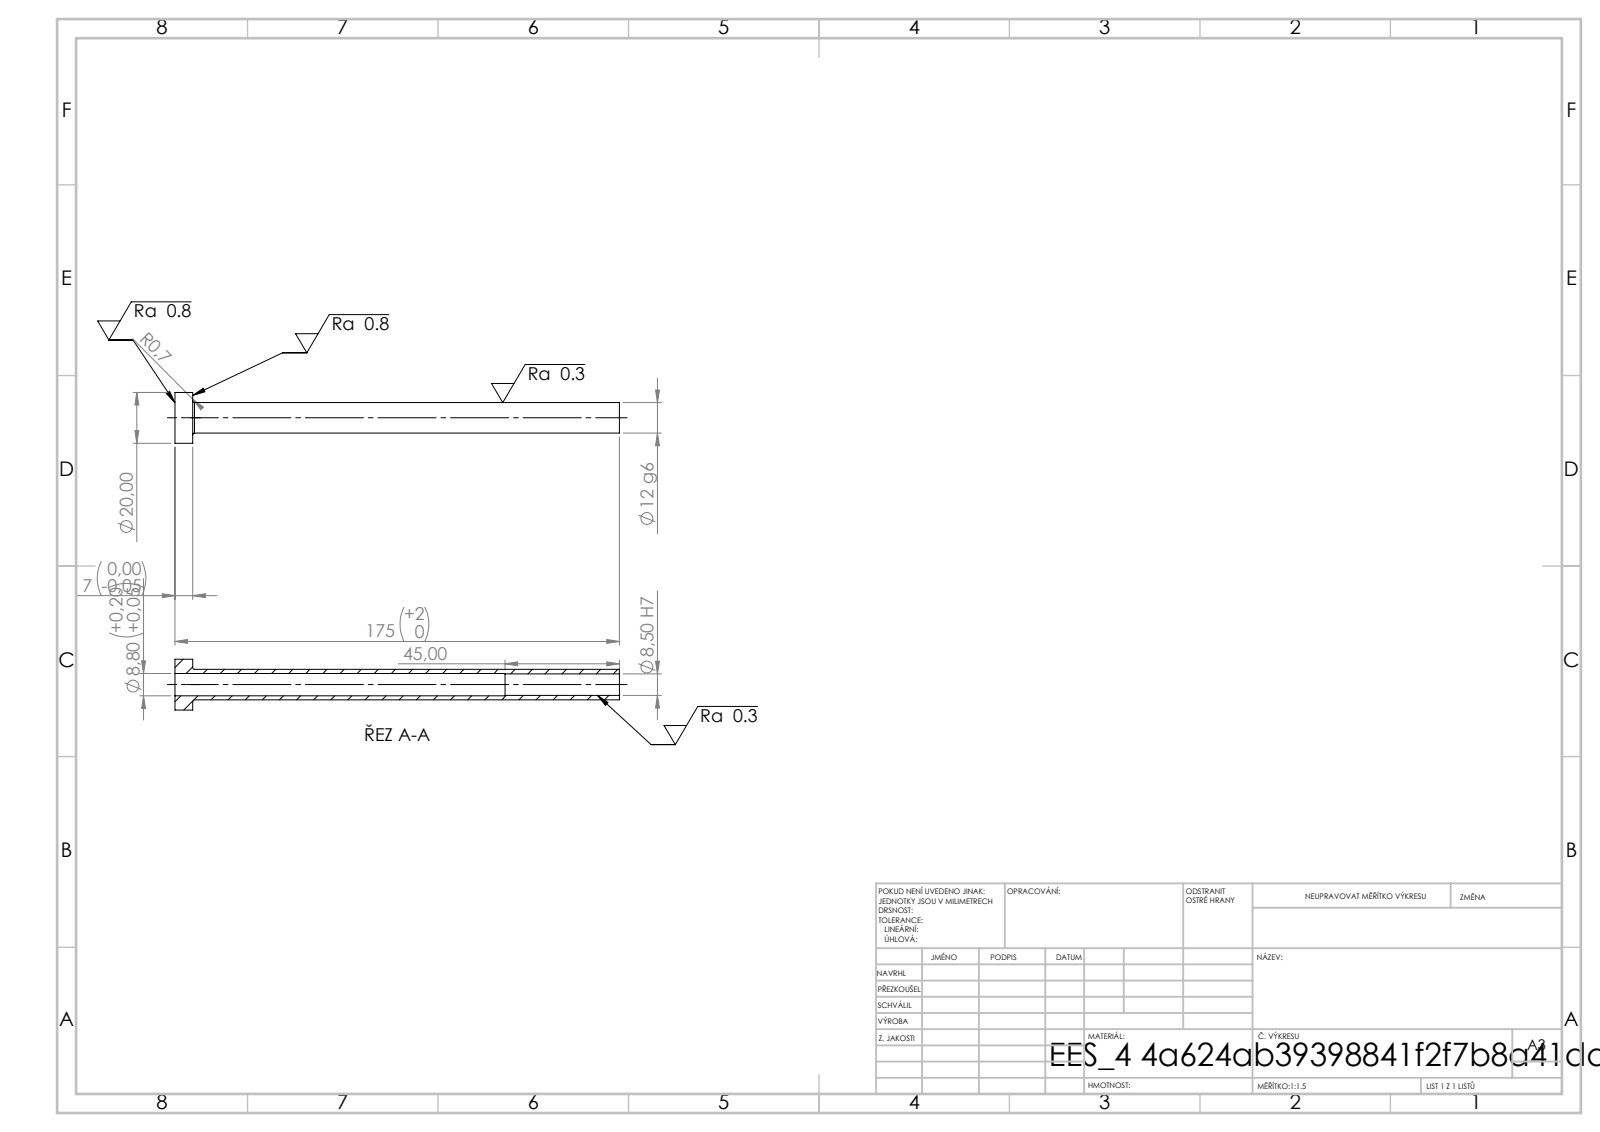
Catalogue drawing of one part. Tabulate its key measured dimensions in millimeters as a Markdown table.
| quantity | value |
| --- | --- |
| STEP written by | SolidWorks 2019 (CONFIG_CONTROL_DESIGN) |
| units | millimeters |
| bodies | 1 solid, 14 faces (4 planar, 8 cylindrical, 2 other) |
| overall size | 175 × 20 × 20 |
| volume | 10 743 mm³ |
| surface area | 12 073 mm² |
| round holes (diameter × count) | 8.5 × 1, 8.8 × 1 |
| round bosses / shafts (diameter × count) | 20 × 1, 12 × 1 |
| main face-to-face distances | 7, 175, 168, 130, 123, 45 |
